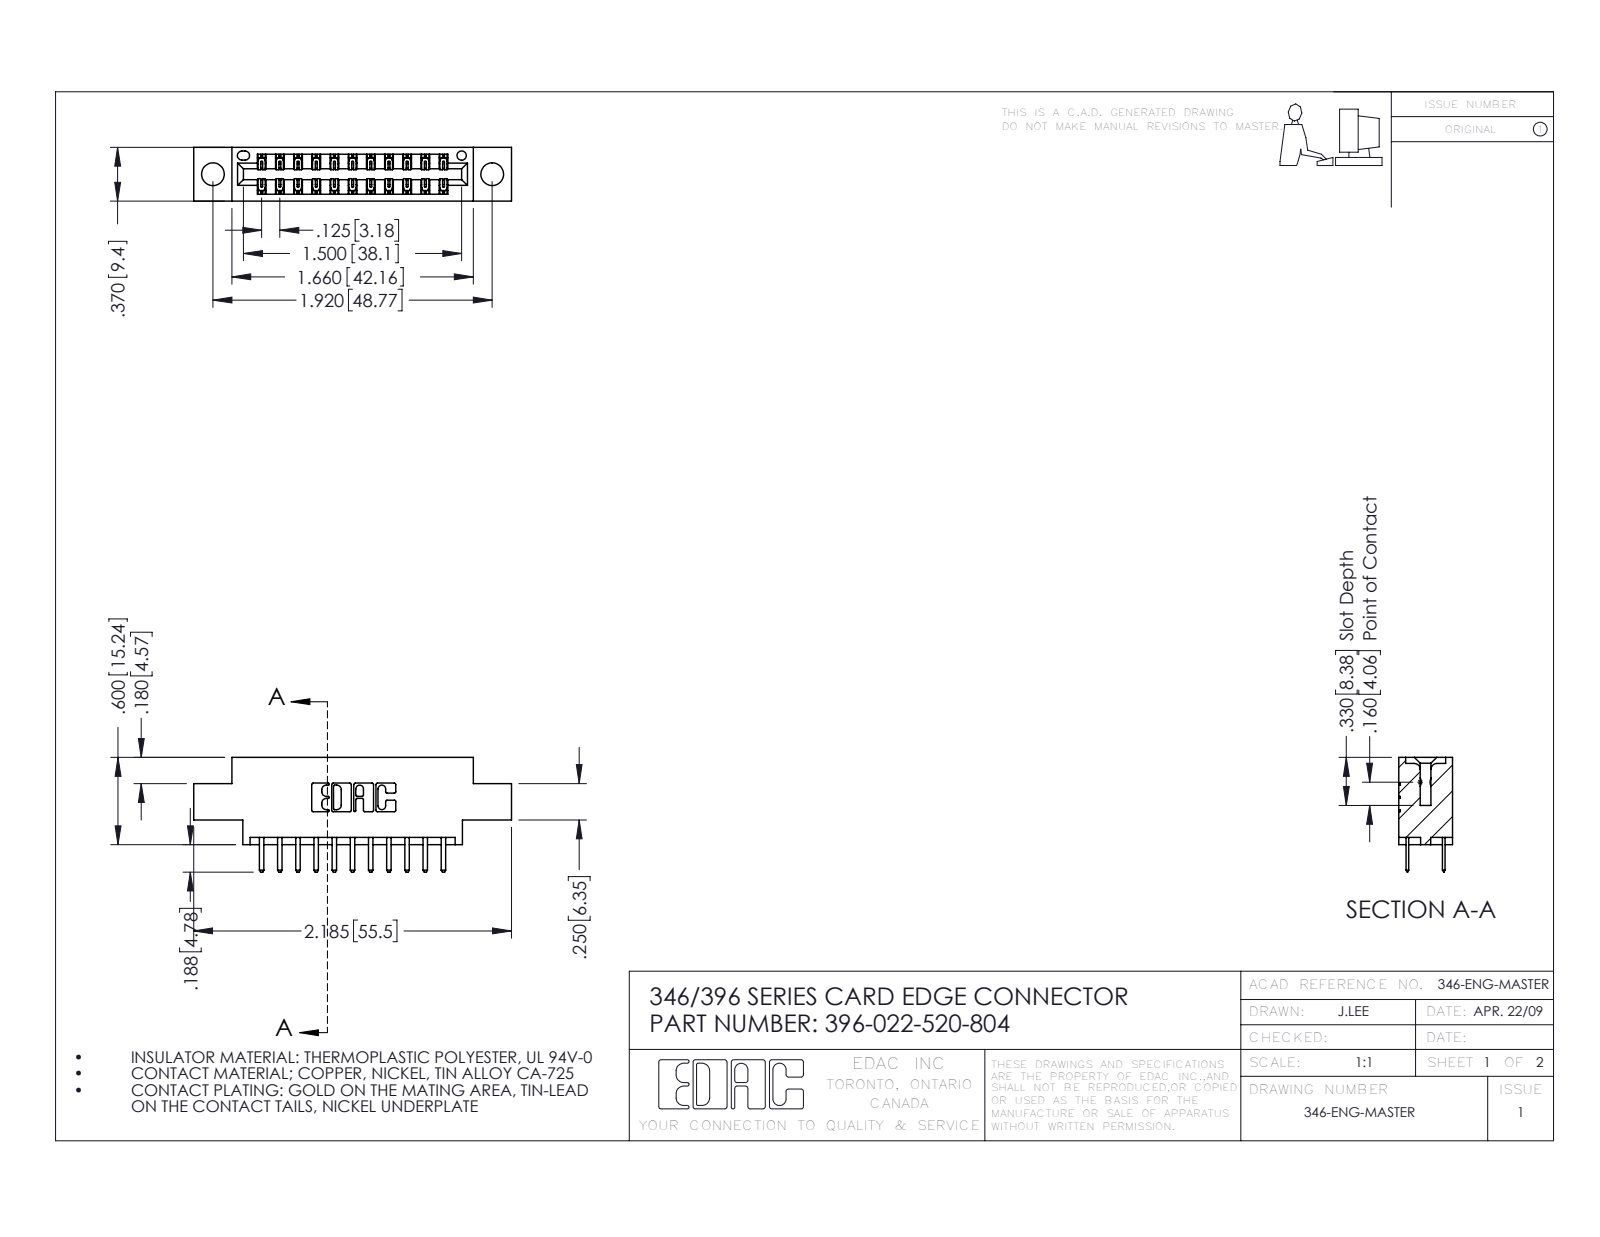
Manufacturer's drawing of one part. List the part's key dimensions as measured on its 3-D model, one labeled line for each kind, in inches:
Part name (STEP PRODUCT): 396-022-520-804; 345-292-001_345-293-120; 346 Part_0.170 Offset - 0.156 Dia-TH
STEP written by: SolidWorks 2016 (CONFIG_CONTROL_DESIGN)
Units: inches
Bodies: 23 solids, 1358 faces (894 planar, 464 cylindrical, 0 other)
Overall size (bounding box): 2.185 × 0.788 × 0.37
Volume: 0.3 in³ · Surface area: 9.679 in²
Round holes (diameter × count): ⌀0.156 ×2, ⌀0.064 ×1
Partial cylindrical surfaces — rounded edges, fillets, slot ends (radius × count): R0.006 ×33, R0.01 ×26, R0.01 ×22, R0.007 ×6, R0.031 ×6, R0.026 ×3, R0.014 ×2, R0.022 ×2
Main face-to-face distances: 0.25, 0.37, 0.048, 0.322, 0.148, 0.222, 0.1, 0.174, 0.275, 0.072
Hole centre spacings: 0.246, 1.715, 1.92
